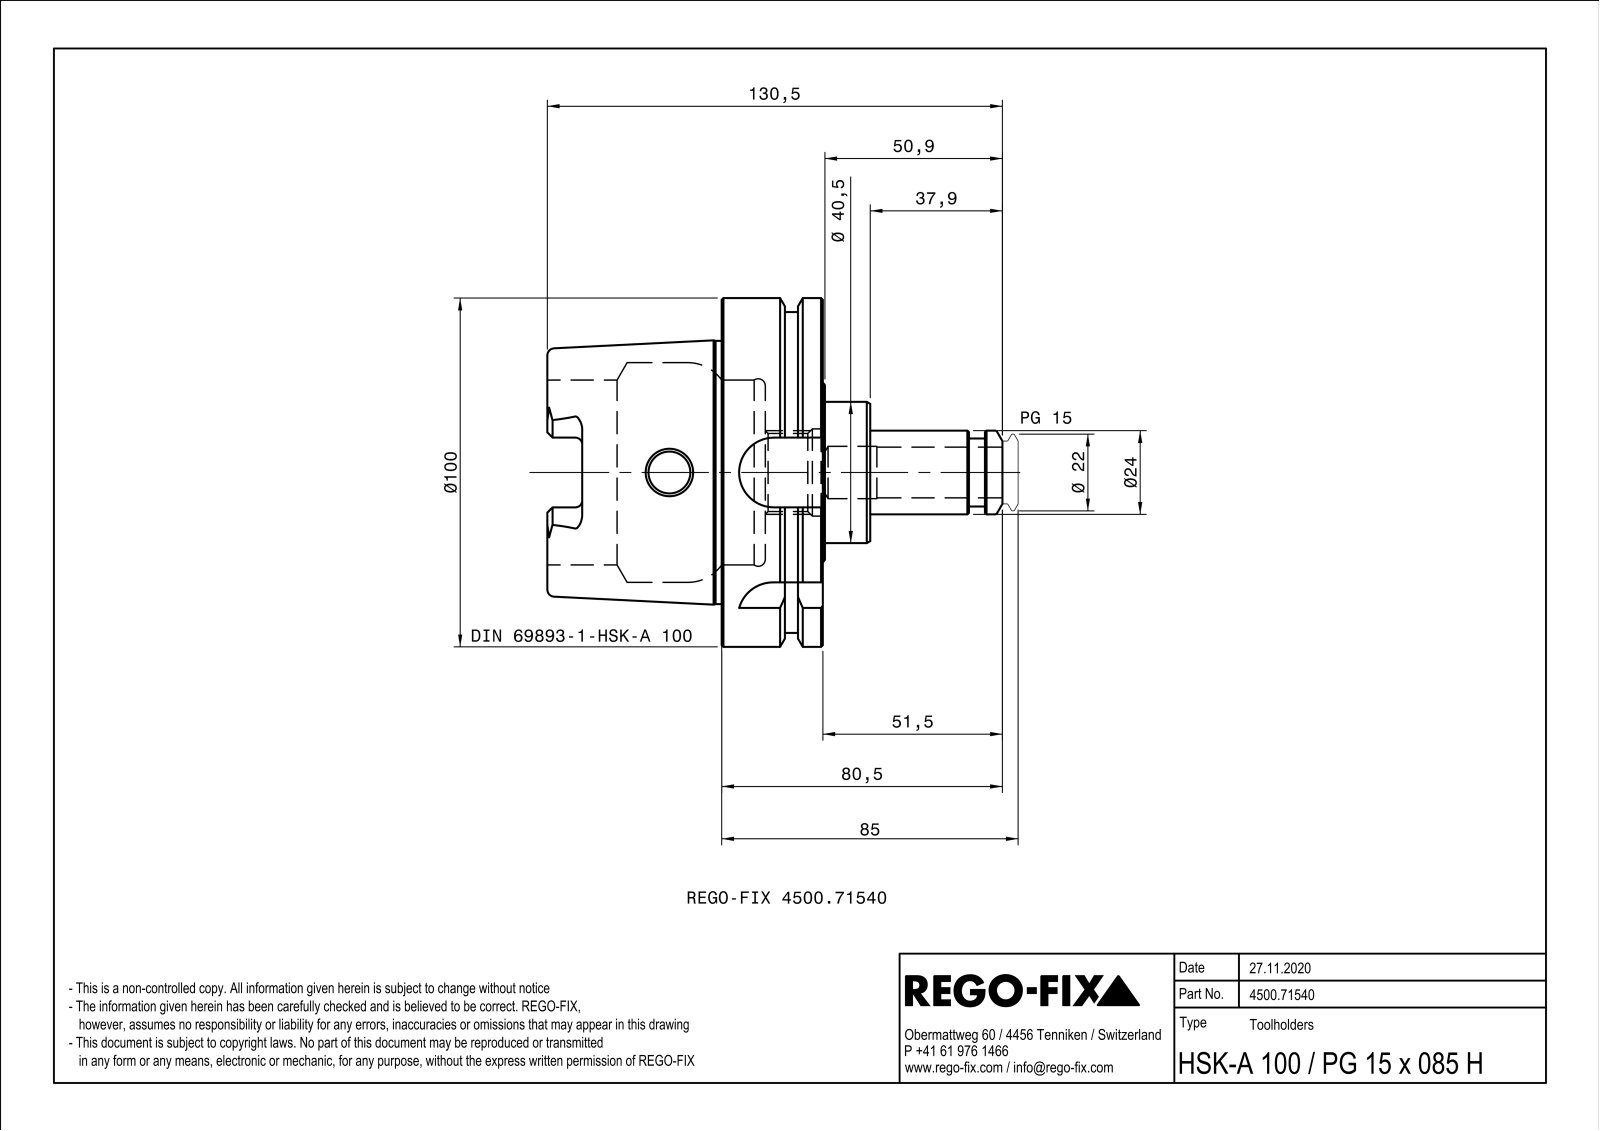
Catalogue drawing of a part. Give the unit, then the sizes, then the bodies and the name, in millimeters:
Units: millimetres
Overall size (bounding box): 130.5 × 100 × 100
Round holes (diameter × count): ⌀5 ×4, ⌀12 ×2, ⌀8.5 ×1, ⌀10 ×1, ⌀15 ×1, ⌀22.38 ×1, ⌀25 ×1, ⌀53 ×1, ⌀63 ×1
Round bosses / shafts (diameter × count): ⌀100 ×1, ⌀92 ×1, ⌀75.46 ×1, ⌀40.5 ×1, ⌀24 ×1, ⌀19.5 ×1
Partial cylindrical surfaces — rounded edges, fillets, slot ends (radius × count): R2 ×6, R4.88 ×4, R10 ×2, R11 ×1
Main face-to-face distances: 29, 12.5, 16.5, 79, 62.5, 50, 13.6, 30.1, 42.6, 92.6
Hole centre spacings: 31, 5.41, 35.57, 39.86
Volume: 277 976 mm³ · Surface area: 57 403 mm²
Bodies: 1 solid, 152 faces (40 planar, 42 cylindrical, 70 other)
Part name (STEP PRODUCT): NOCUT
STEP written by: SIEMENS PLM Software Solid Edge ST10 (AUTOMOTIVE_DESIGN)
